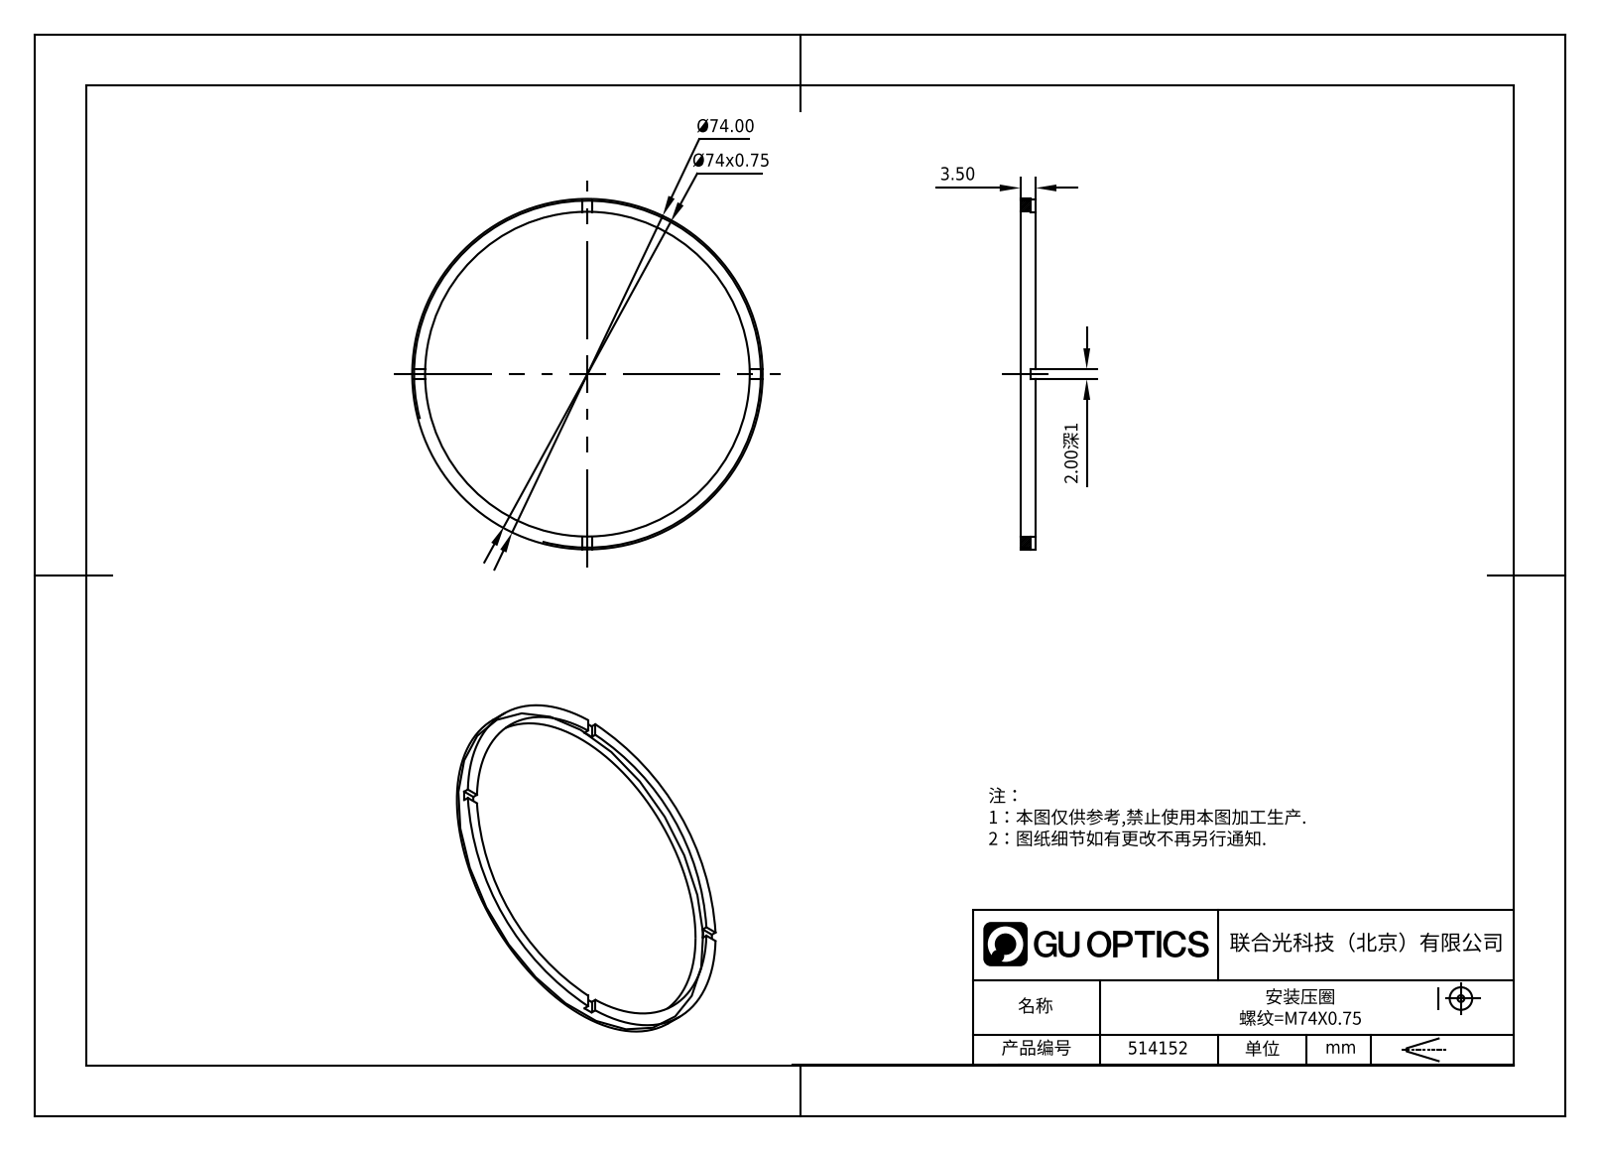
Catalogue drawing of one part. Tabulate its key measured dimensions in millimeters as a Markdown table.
| quantity | value |
| --- | --- |
| part name | 514152 |
| STEP written by | SolidWorks 2020 (CONFIG_CONTROL_DESIGN) |
| units | millimeters |
| bodies | 1 solid, 21 faces (17 planar, 4 cylindrical, 0 other) |
| overall size | 74 × 74 × 3.5 |
| volume | 2 318 mm³ |
| surface area | 2 908 mm² |
| round holes (diameter × count) | 68 × 1 |
| round bosses / shafts (diameter × count) | 74 × 1 |
| main face-to-face distances | 3.5, 2.5, 1, 2 |
